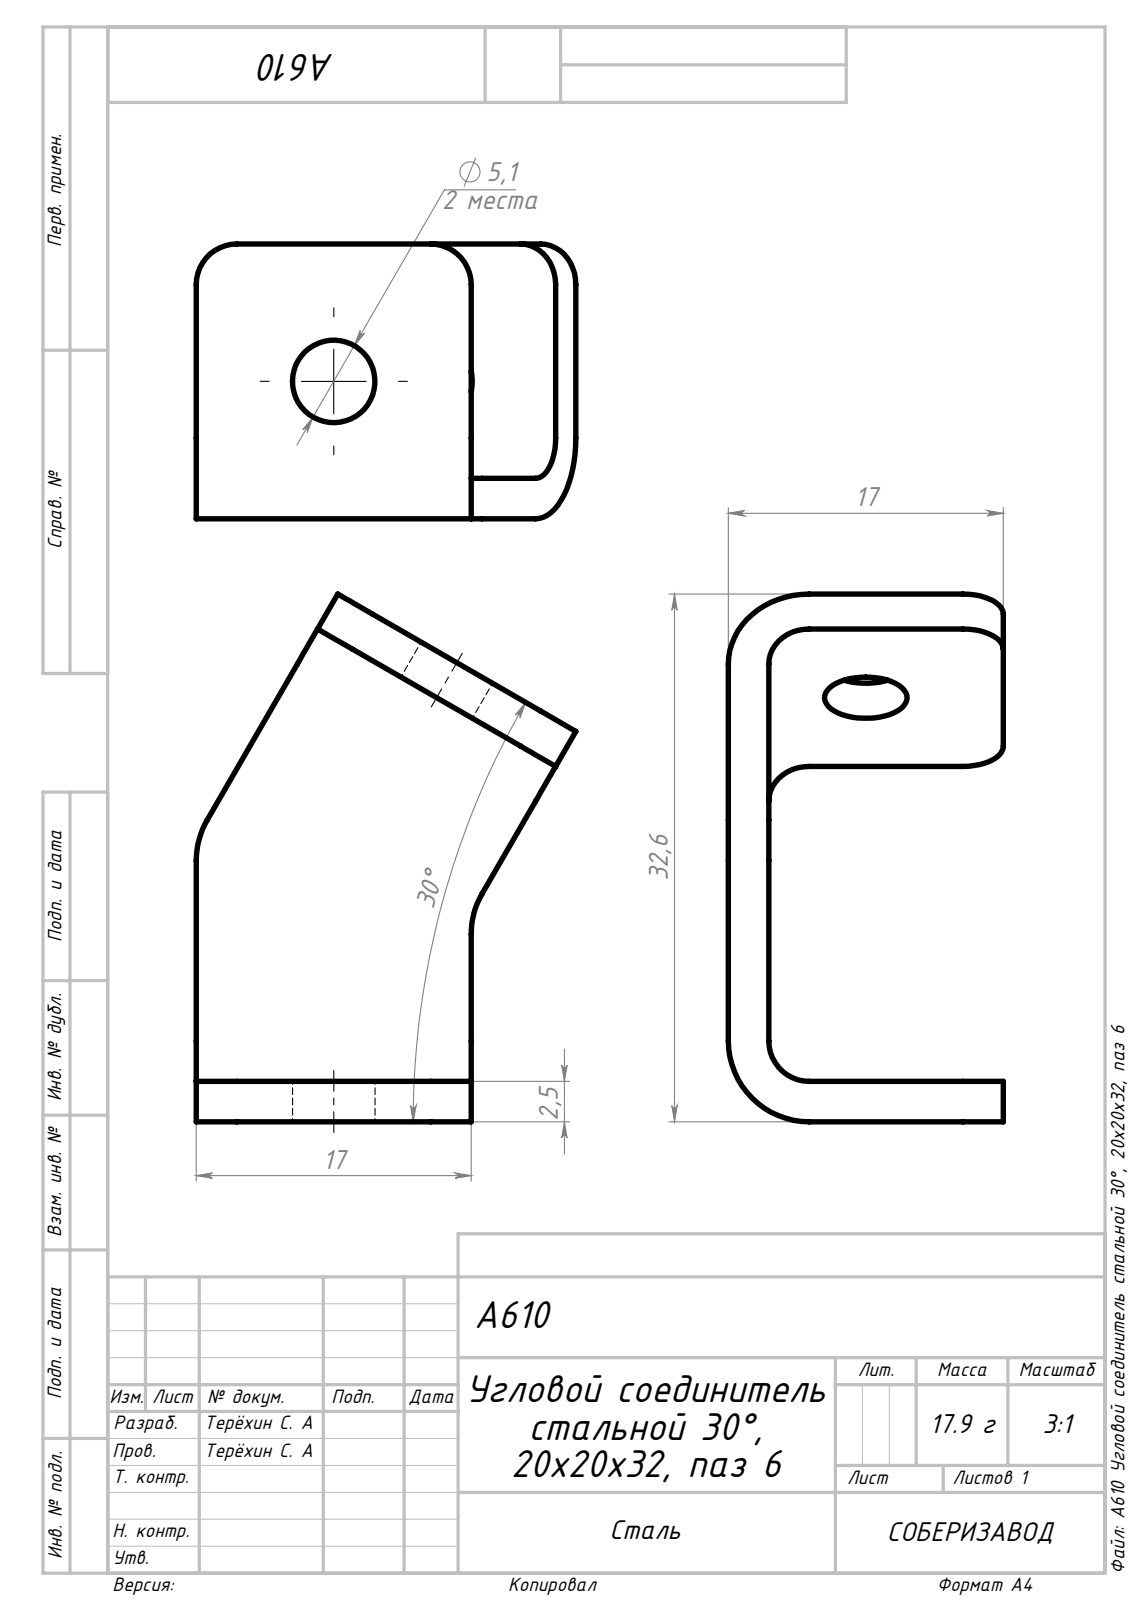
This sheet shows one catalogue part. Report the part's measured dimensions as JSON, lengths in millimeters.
{"step_written_by": "SolidWorks 2021 (AUTOMOTIVE_DESIGN)", "units": "millimeters", "bodies": {"solids": 1, "faces": 34, "planar": 20, "cylindrical": 14, "other": 0}, "overall_size": [32.66, 23.47, 17], "volume_mm3": 2274, "surface_area_mm2": 2254, "round_holes": [[5.1, 2]], "partial_cylinders_radius": [[2.5, 6], [5, 4]], "face_to_face_distances": [2.5, 17, 14.5]}
